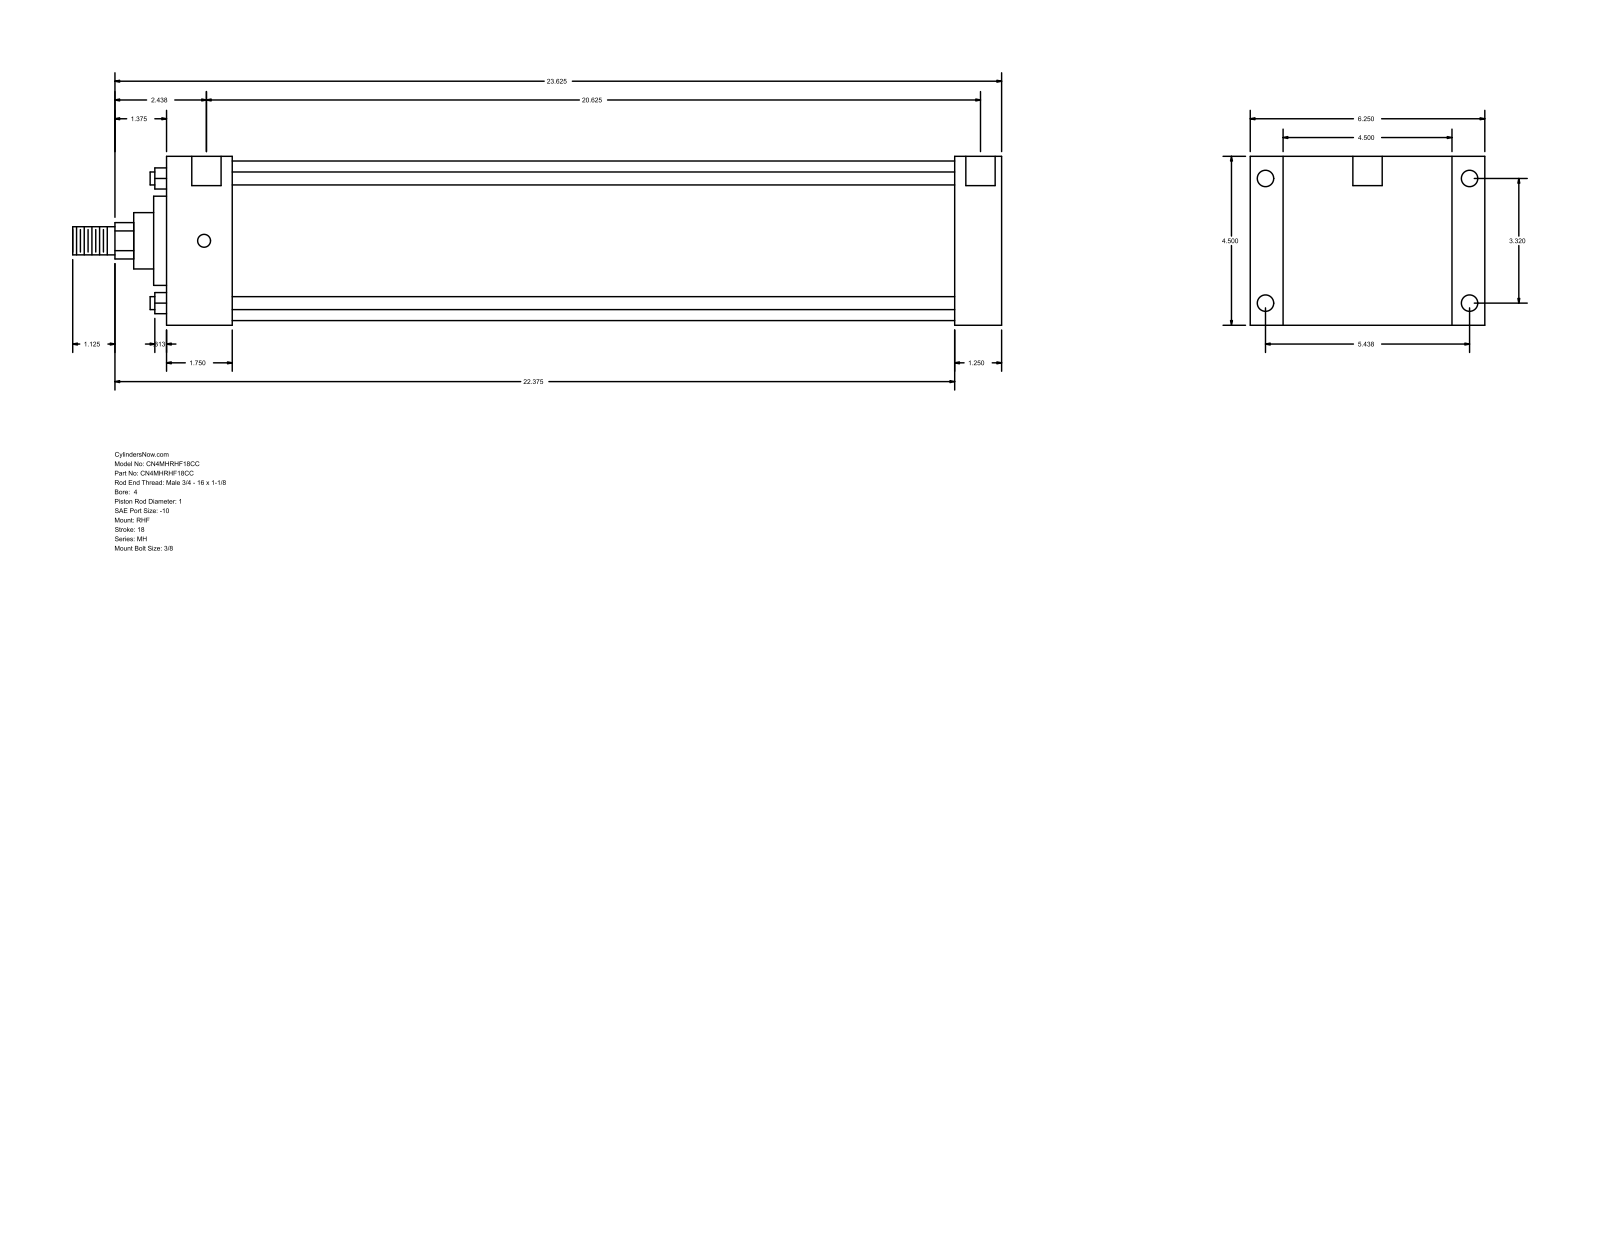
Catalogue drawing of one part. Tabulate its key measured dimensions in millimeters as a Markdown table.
| quantity | value |
| --- | --- |
| part name | MH_RHF__0400_1 |
| STEP written by | GSSL Pune (CONFIG_CONTROL_DESIGN) |
| units | millimeters |
| bodies | 0 solids, 90 faces (61 planar, 29 cylindrical, 0 other) |
| overall size | 628.65 × 158.75 × 114.3 |
| round holes (diameter × count) | 8.73 × 4, 11.13 × 4, 19.84 × 2 |
| round bosses / shafts (diameter × count) | 8.76 × 4, 107.95 × 1, 60.33 × 1, 38.1 × 1, 25.4 × 1, 19.05 × 1 |
| partial cylindrical surfaces (radius × count) | 12.29 × 1 |
| main face-to-face distances | 114.3, 565.16, 533.41, 31.75, 22.23, 136.53, 44.46, 488.95, 520.7, 158.76 |
| hole center spacings | 84.32, 138.12, 161.82, 527.05, 1.58, 1.59, 523.88, 525.46 |
